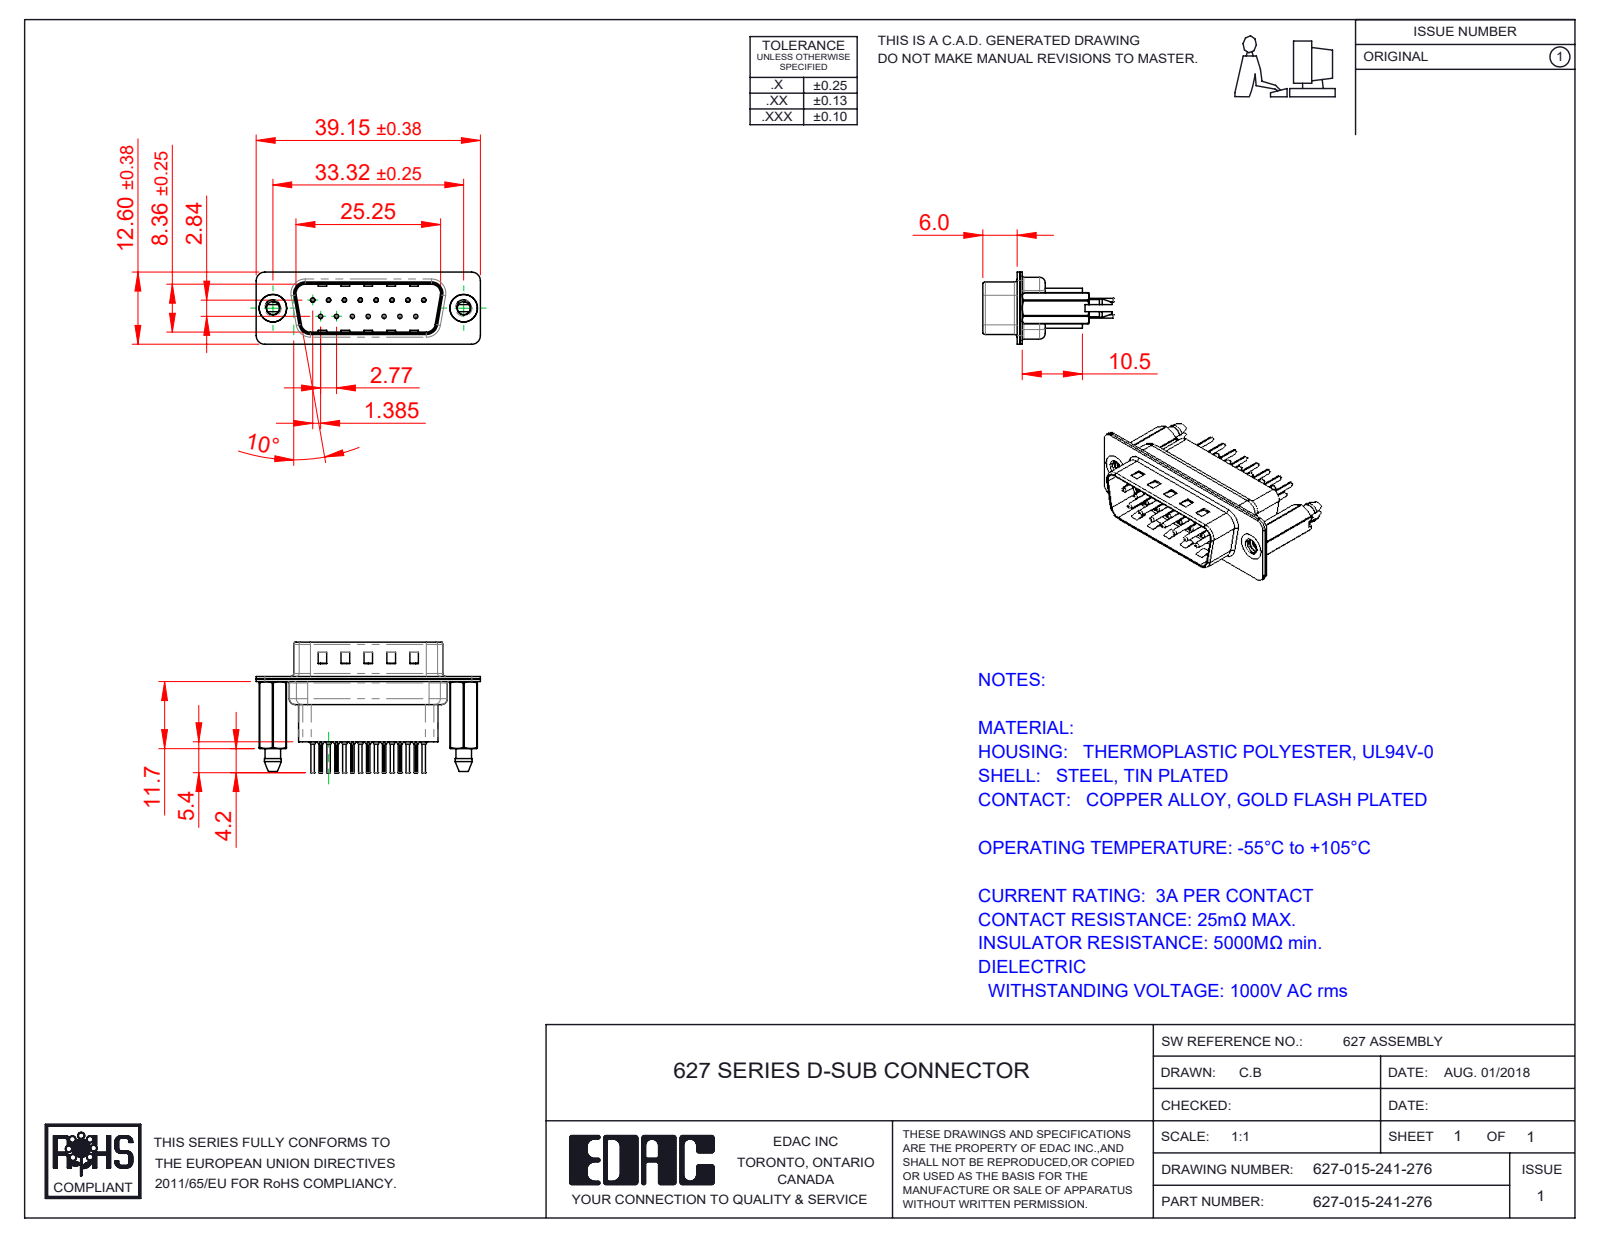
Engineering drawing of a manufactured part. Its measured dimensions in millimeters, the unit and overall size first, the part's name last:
Units: millimetres
Overall size (bounding box): 39.15 × 22.8 × 12.6
Round holes (diameter × count): ⌀0.2 ×15, ⌀0.35 ×15, ⌀1.1 ×15, ⌀1.6 ×15, ⌀2.26 ×2, ⌀4 ×2, ⌀4.8 ×2
Round bosses / shafts (diameter × count): ⌀2 ×15, ⌀1.5 ×15, ⌀0.75 ×15, ⌀0.6 ×15, ⌀4.9 ×2
Partial cylindrical surfaces — rounded edges, fillets, slot ends (radius × count): R0.1 ×30, R1.5 ×18, R2 ×12, R1.6 ×10, R0.5 ×8, R0.25 ×4, R0.6 ×4, R0.65 ×4
Main face-to-face distances: 0.4, 0.45, 0.9, 0.82, 9.58, 1.5, 0.68, 7.68, 1.4, 1.08
Hole centre spacings: 3.16, 2.77, 5.54, 8.31, 11.08, 5.03, 5.04, 7.48
Volume: 2 826 mm³ · Surface area: 7 322 mm²
Bodies: 20 solids, 1918 faces (531 planar, 754 cylindrical, 633 other)
Part name (STEP PRODUCT): 627 Shell Rear_15 Contacts; 627 Shell Front_15 Contacts; 627 Contact Row 1_41; 627 4-40 Threaded Boardlock_HP41 (+3 more)
STEP written by: SolidWorks 2020 (CONFIG_CONTROL_DESIGN)
